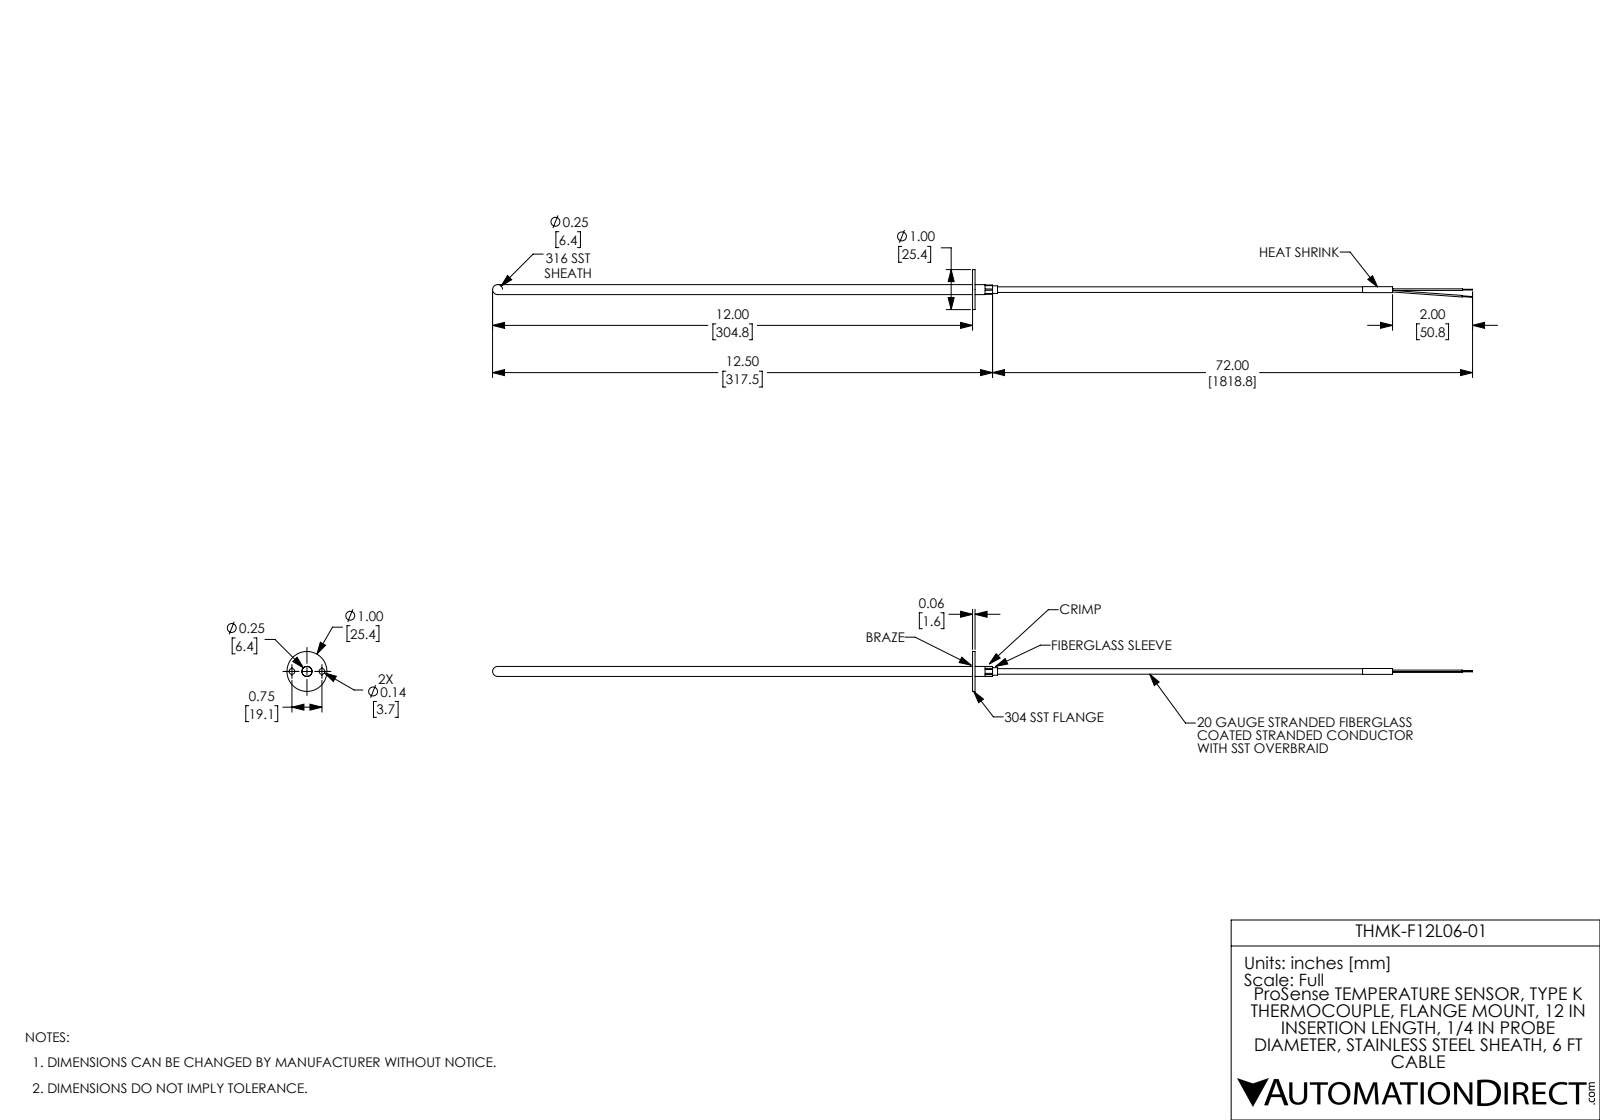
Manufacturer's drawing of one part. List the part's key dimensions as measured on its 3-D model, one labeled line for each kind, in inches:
Part name (STEP PRODUCT): THMJ-F12L06-02
STEP written by: SolidWorks 2017 (AUTOMOTIVE_DESIGN)
Units: inches
Bodies: 7 solids, 65 faces (30 planar, 32 cylindrical, 3 other)
Overall size (bounding box): 24.5 × 1 × 1
Volume: 0.826 in³ · Surface area: 26.97 in²
Round holes (diameter × count): ⌀0.144 ×3, ⌀0.136 ×1, ⌀0.189 ×1, ⌀0.257 ×1
Round bosses / shafts (diameter × count): ⌀1 ×1, ⌀0.25 ×1, ⌀0.19 ×1, ⌀0.188 ×1, ⌀0.148 ×1, ⌀0.14 ×1, ⌀0.132 ×1, ⌀0.04 ×1
Main face-to-face distances: 0.063, 0.5, 0.437, 0.231, 0.75, 0.125, 0.188, 0.625, 0.625, 0.562
Hole centre spacings: 0.375, 0.375, 0.75
